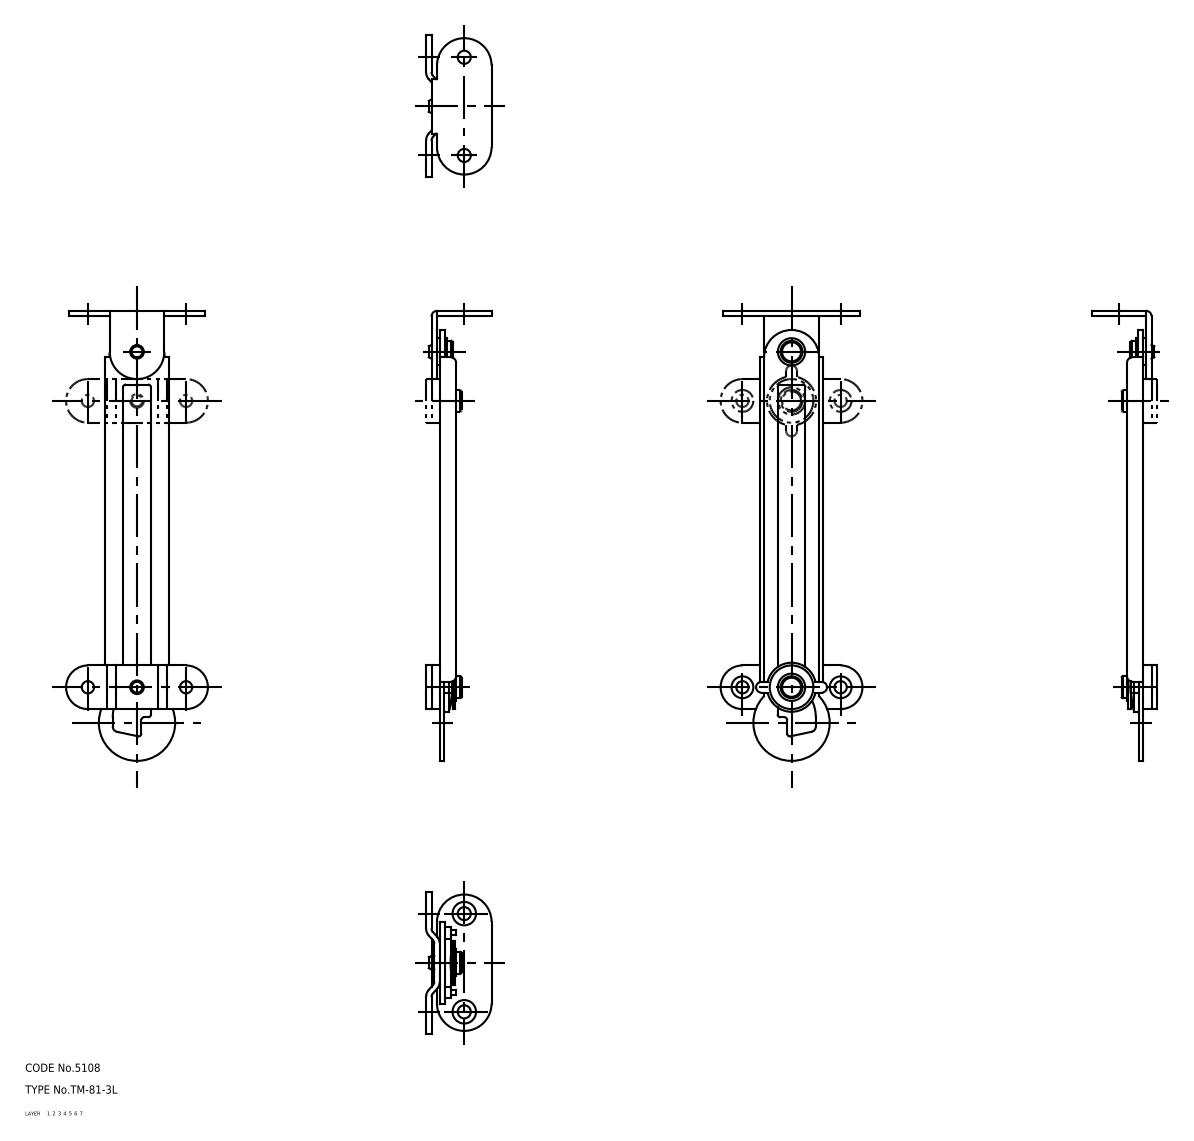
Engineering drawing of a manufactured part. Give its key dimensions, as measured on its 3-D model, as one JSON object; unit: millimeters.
{"part_name": "67118480; 67118493; 67118506; 67118519 (+7 more)", "step_written_by": "CADfix (AUTOMOTIVE_DESIGN)", "units": "millimeters", "bodies": {"solids": 11, "faces": 160, "planar": 0, "cylindrical": 0, "other": 160}, "overall_size": [165, 52, 24], "volume_mm3": 10143, "surface_area_mm2": 14805}
